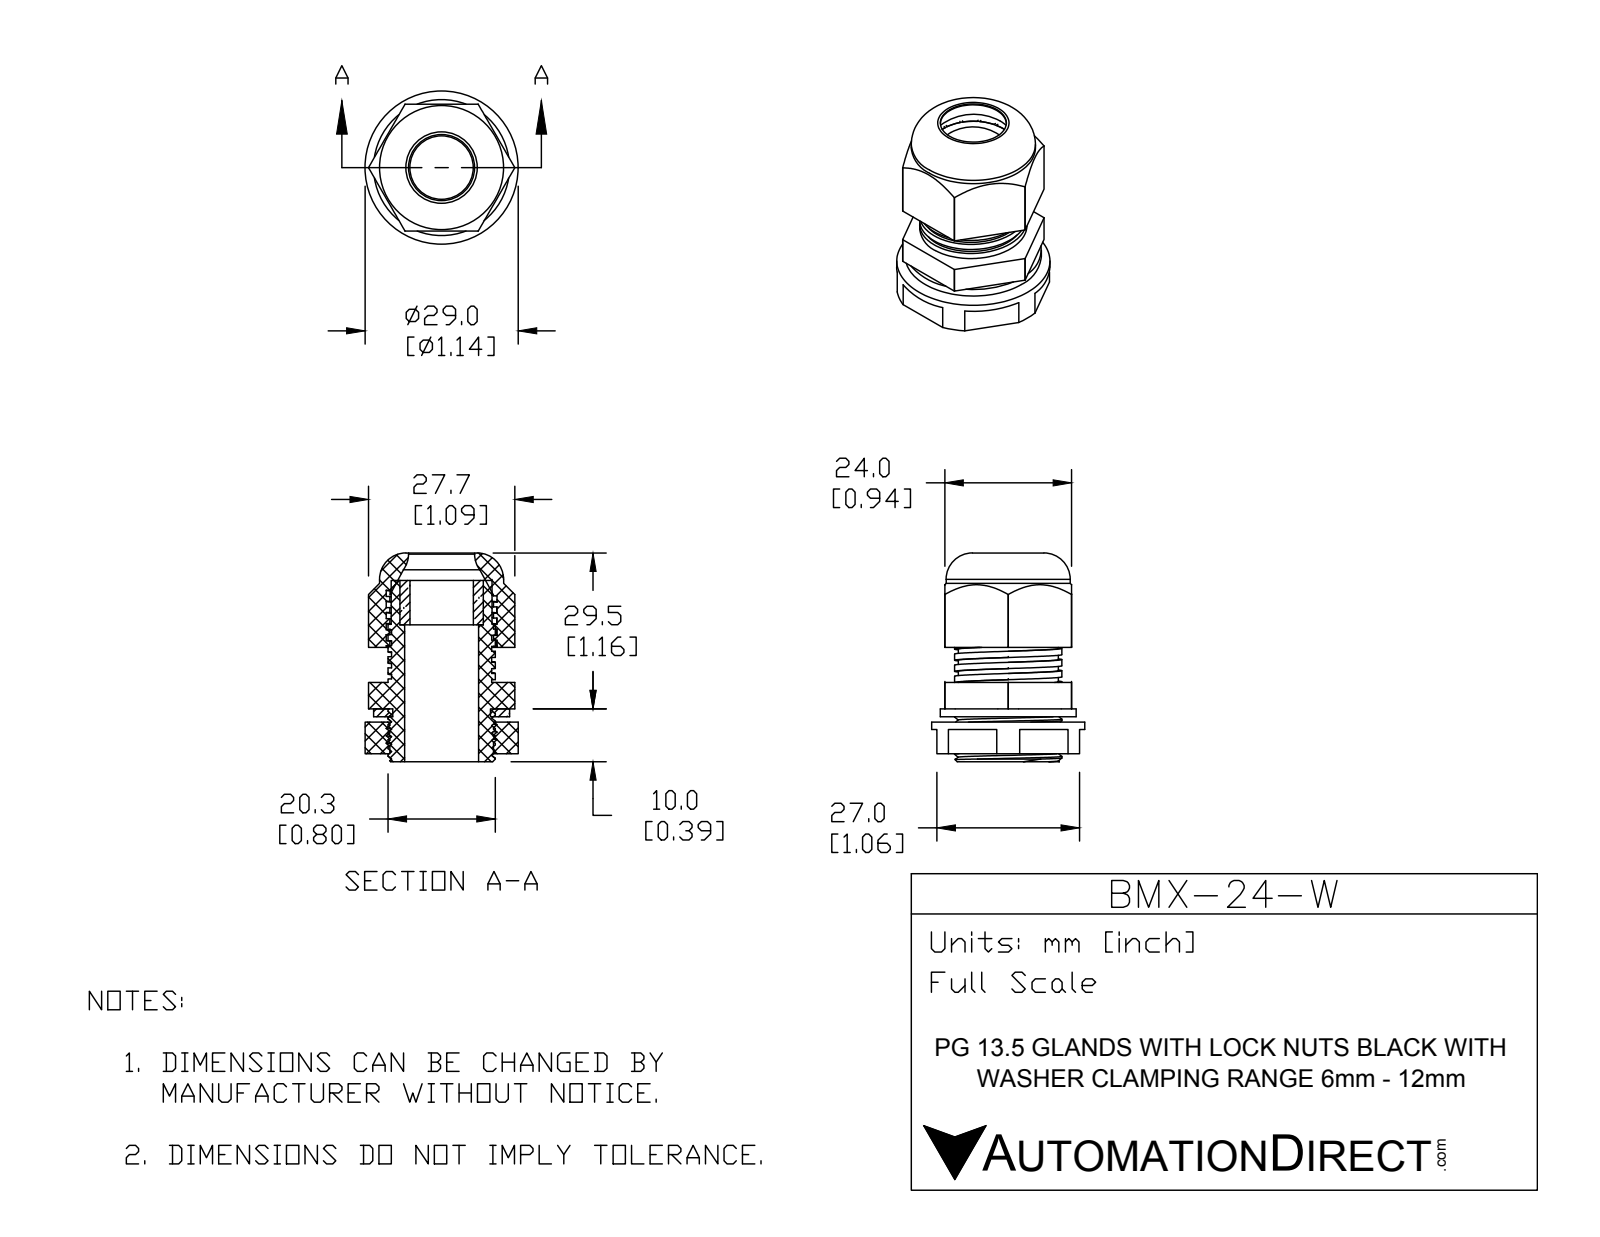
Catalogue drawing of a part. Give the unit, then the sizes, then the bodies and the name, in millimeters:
Units: millimetres
Overall size (bounding box): 39.5 × 29 × 29
Round holes (diameter × count): ⌀12 ×1, ⌀12.5 ×1, ⌀14 ×1, ⌀15.8 ×1, ⌀18.5 ×1, ⌀19.63 ×1
Round bosses / shafts (diameter × count): ⌀29 ×1, ⌀25.75 ×1, ⌀23.5 ×1, ⌀20.3 ×1, ⌀19.1 ×1
Partial cylindrical surfaces — rounded edges, fillets, slot ends (radius × count): R13.85 ×1
Main face-to-face distances: 1.5, 24, 8.5, 2.5, 7.5, 6, 25.5, 7, 1, 13.5
Volume: 11 918 mm³ · Surface area: 11 993 mm²
Bodies: 5 solids, 200 faces (100 planar, 78 cylindrical, 22 other)
Part name (STEP PRODUCT): BMX-24-W
STEP written by: SolidWorks 2015 (CONFIG_CONTROL_DESIGN)
